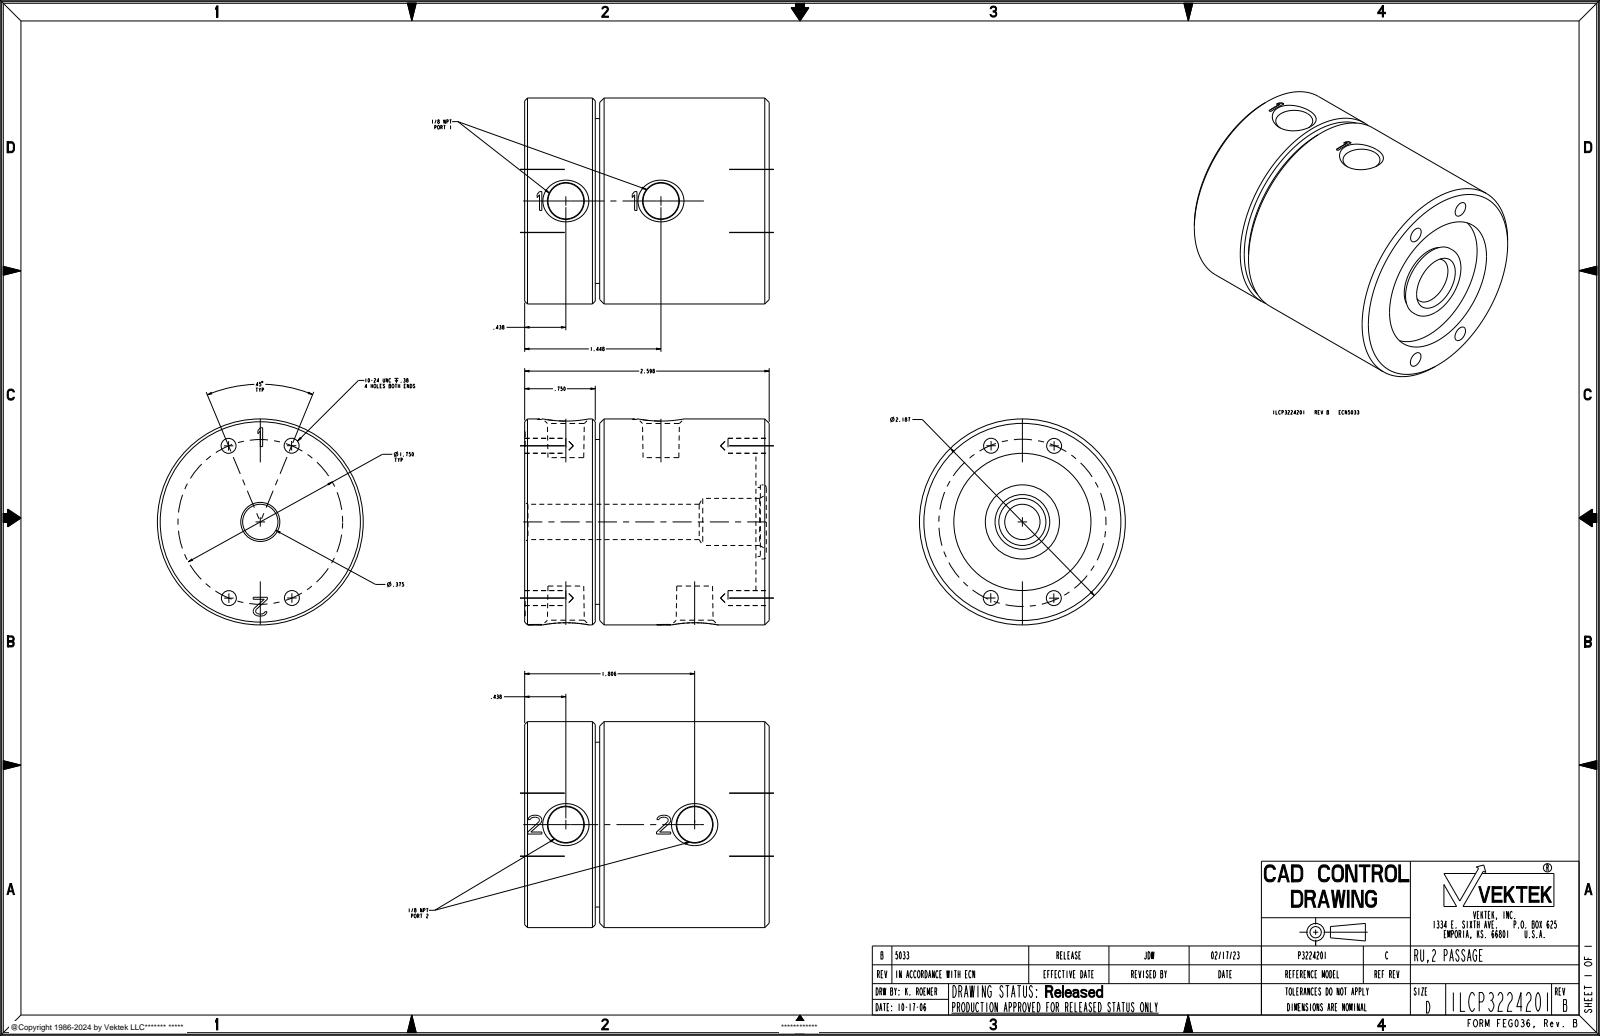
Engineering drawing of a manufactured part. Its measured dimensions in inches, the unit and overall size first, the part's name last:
Units: inches
Overall size (bounding box): 2.598 × 2.187 × 2.187
Round holes (diameter × count): ⌀0.159 ×4, ⌀0.375 ×1, ⌀0.5 ×1, ⌀1.457 ×1
Round bosses / shafts (diameter × count): ⌀2.187 ×1, ⌀1.75 ×1, ⌀0.787 ×1, ⌀0.733 ×1
Main face-to-face distances: 2.598, 2.457, 0.141, 1.707, 0.75, 1.848, 0.047, 0.797, 1.66, 1.801
Hole centre spacings: 0.67, 0.875, 0.875, 1.617, 1.75, 1.75
Volume: 8.875 in³ · Surface area: 35 in²
Bodies: 1 solid, 220 faces (122 planar, 48 cylindrical, 50 other)
Part name (STEP PRODUCT): ILCP3224201
STEP written by: CREO PARAMETRIC BY PTC INC, 2021164 (AUTOMOTIVE_DESIGN)
